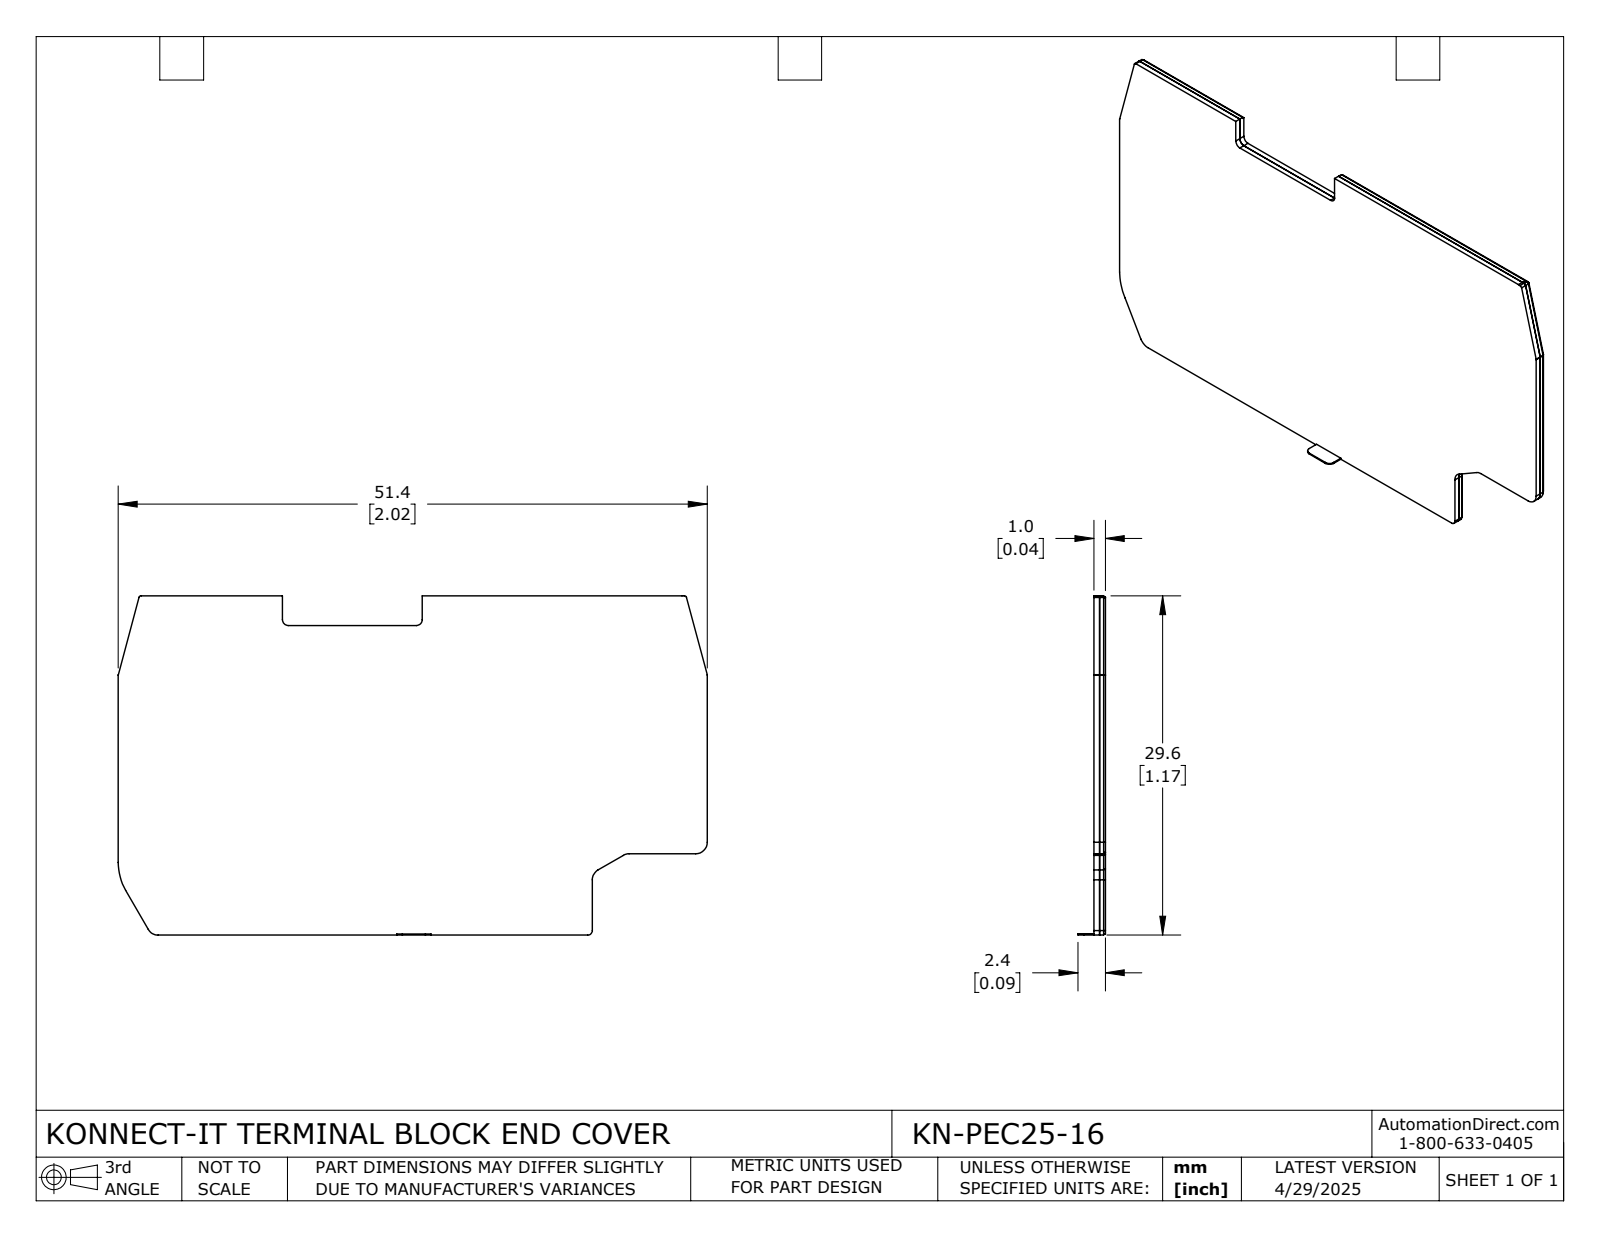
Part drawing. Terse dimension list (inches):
name: KN-PEC25-16
written by: SolidWorks 2024 (CONFIG_CONTROL_DESIGN)
unit: in
bodies: 2 solids, 86 faces (50 planar, 36 cylindrical, 0 other)
size: 2.025 × 1.166 × 0.094
volume: 0.085 in³; area: 8.953 in²
rounds: 4× R0.004, 4× R0.008, 4× R0.02, 4× R0.039, 2× R0.035, 2× R0.043, 1× R0.012, 1× R0.016
face distances: 0.02, 0.039, 1.166, 1.162, 0.033, 0.014, 2.025, 1.064, 0.102, 1.06
